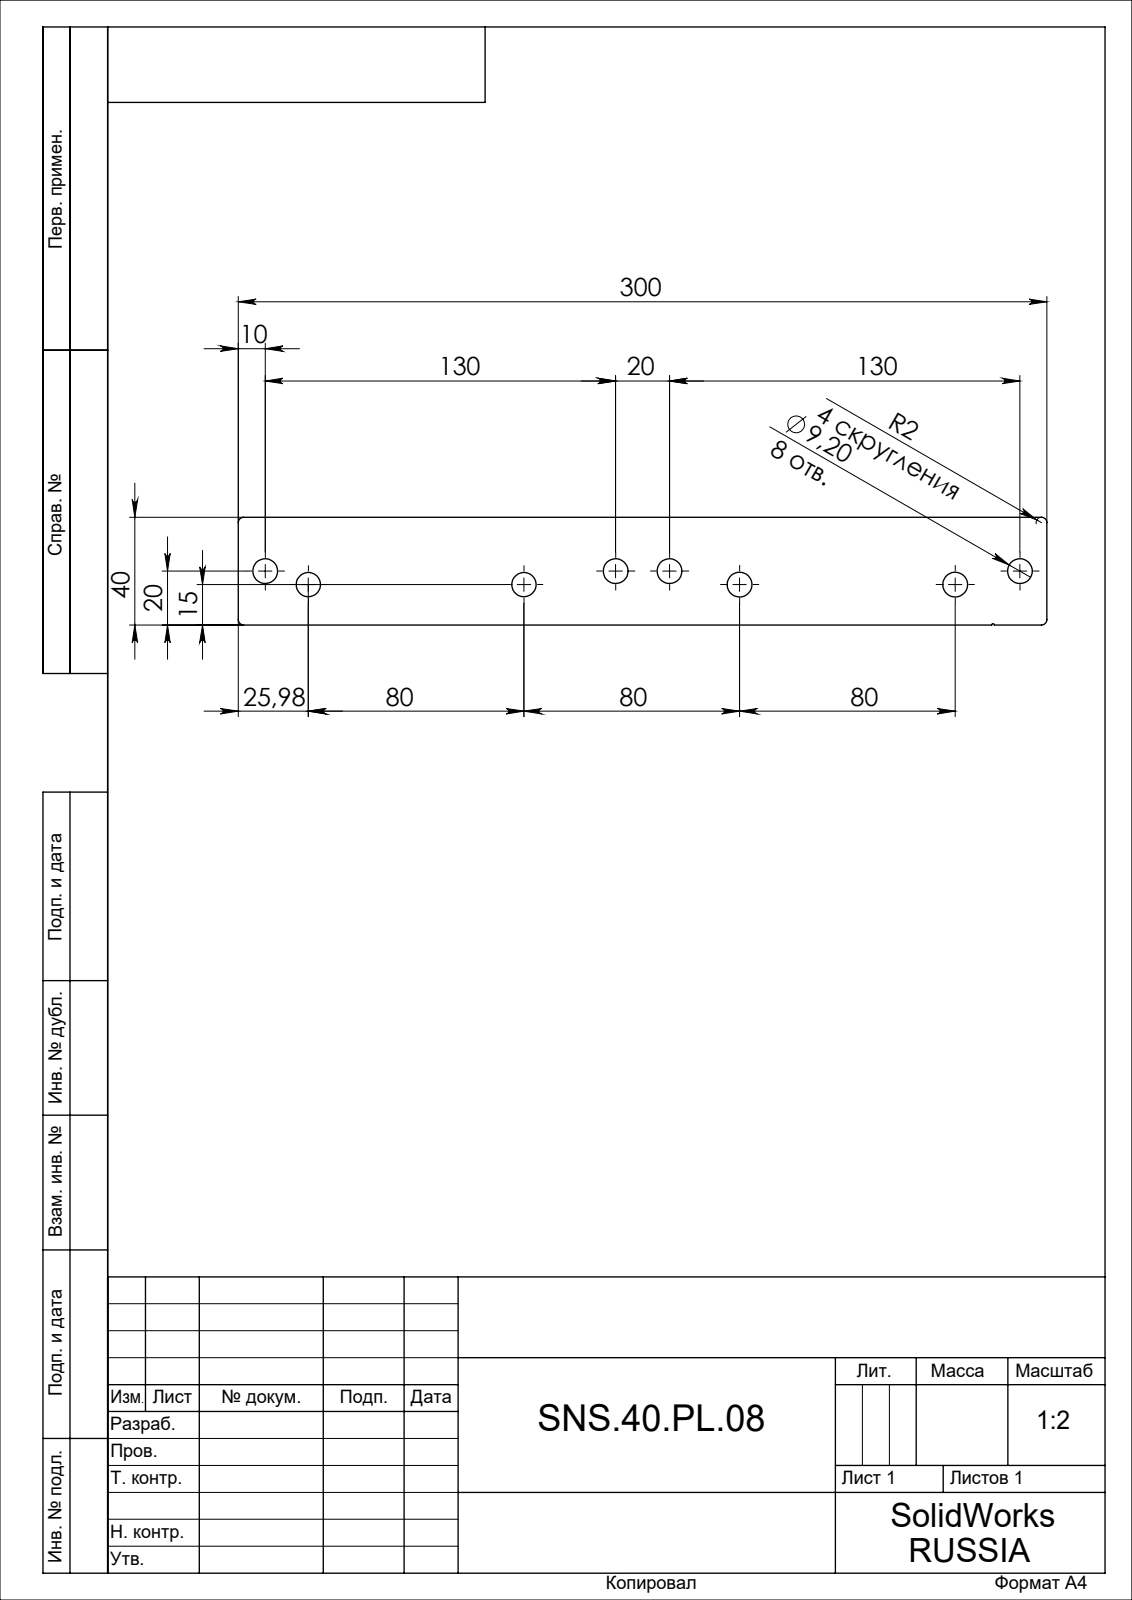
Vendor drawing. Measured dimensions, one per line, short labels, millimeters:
written by: SolidWorks 2018 (AUTOMOTIVE_DESIGN)
unit: mm
bodies: 1 solid, 28 faces (7 planar, 21 cylindrical, 0 other)
size: 300 × 40 × 5
volume: 57 350 mm³; area: 27 476 mm²
holes: 6× ⌀9.2, 2× ⌀9
rounds: 4× R2, 1× R0.5
face distances: 5, 40, 300
hole spacings: 80, 130, 150, 160, 16.74, 20, 24.53, 26.46
